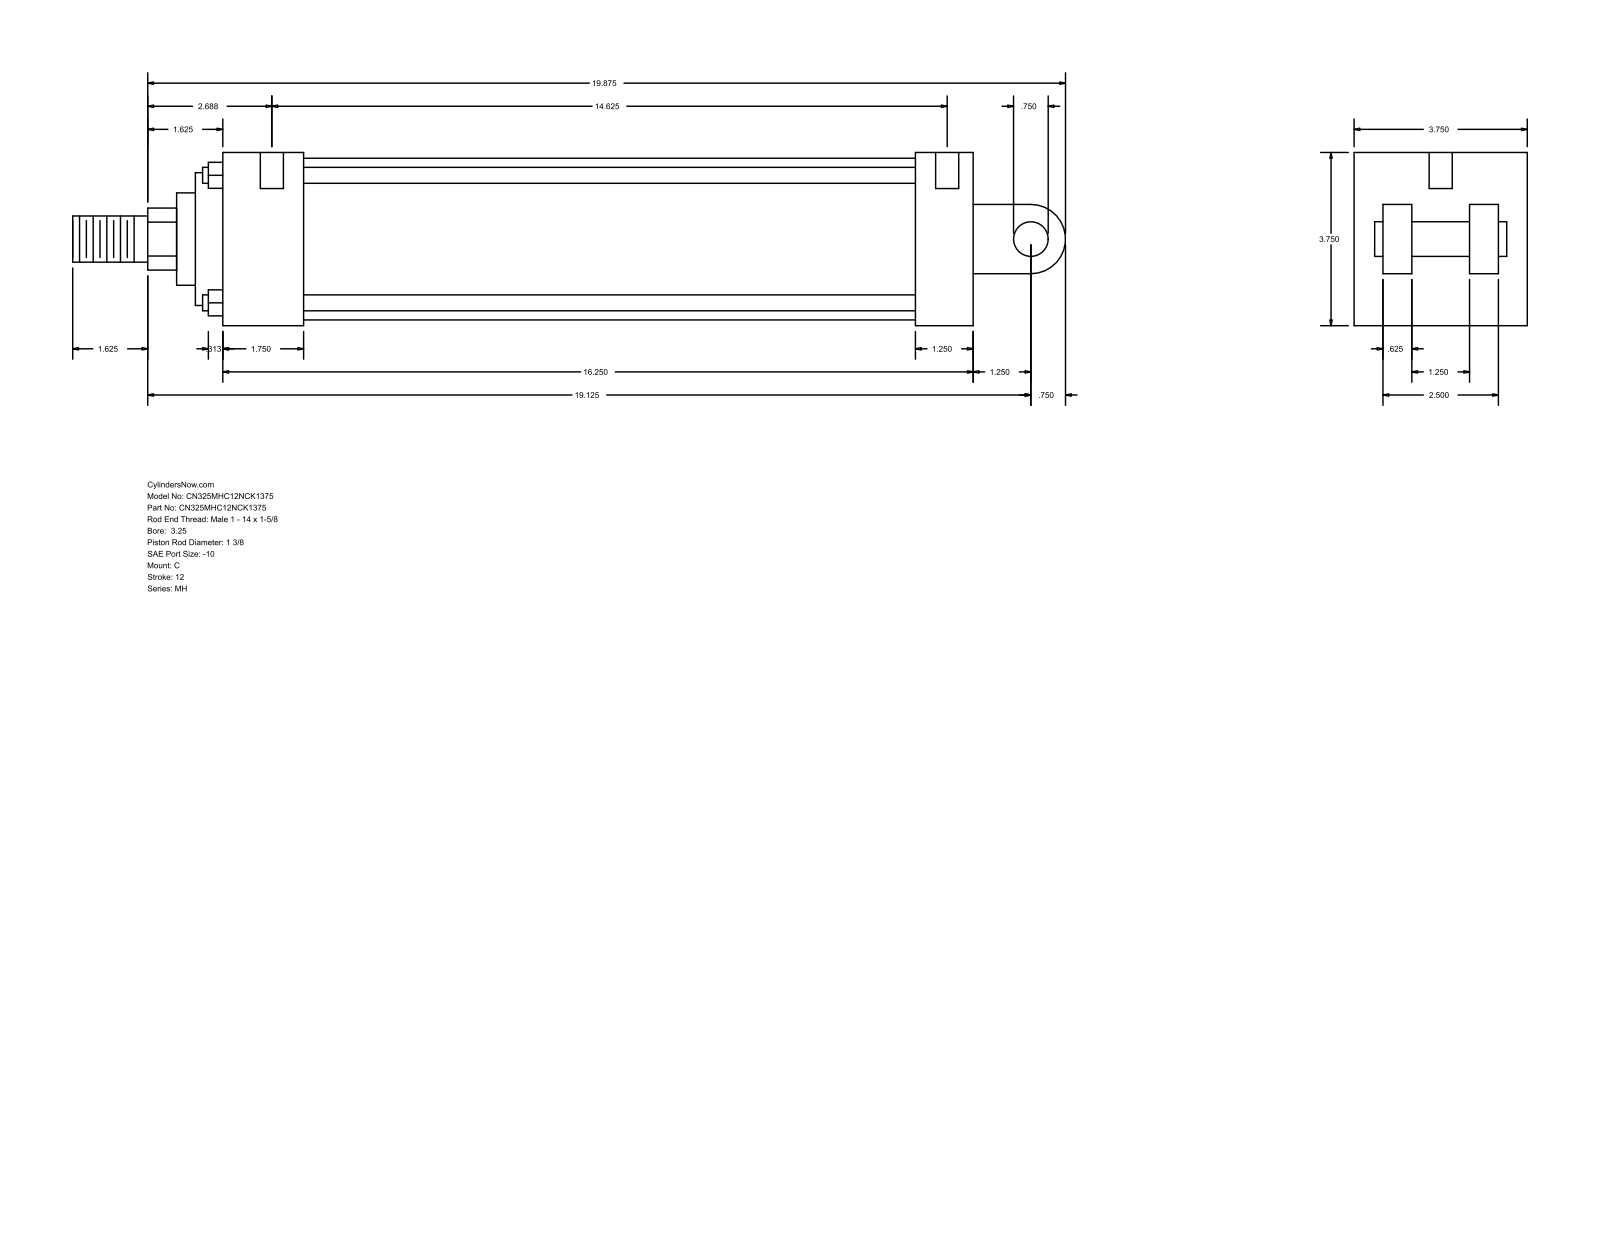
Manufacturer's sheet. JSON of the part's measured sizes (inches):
{"part_name": "MH_C__0325_1.375", "step_written_by": "GSSL Pune (CONFIG_CONTROL_DESIGN)", "units": "inches", "bodies": {"solids": 0, "faces": 101, "planar": 71, "cylindrical": 30, "other": 0}, "overall_size": [21.5, 3.75, 3.75], "round_holes": [[0.219, 4], [0.5, 2]], "round_bosses_or_shafts": [[0.345, 4], [3.5, 1], [2.875, 1], [2, 1], [1.375, 1], [1, 1], [0.75, 1]], "partial_cylinders_radius": [[0.672, 1], [0.75, 1]], "face_to_face_distances": [3.75, 0.625, 2.5, 16.25, 3.125, 1.25, 1.875, 1.75, 15, 13.25], "hole_center_spacings": [14.875, 0.063, 0.187, 14.625, 14.688, 14.813]}
